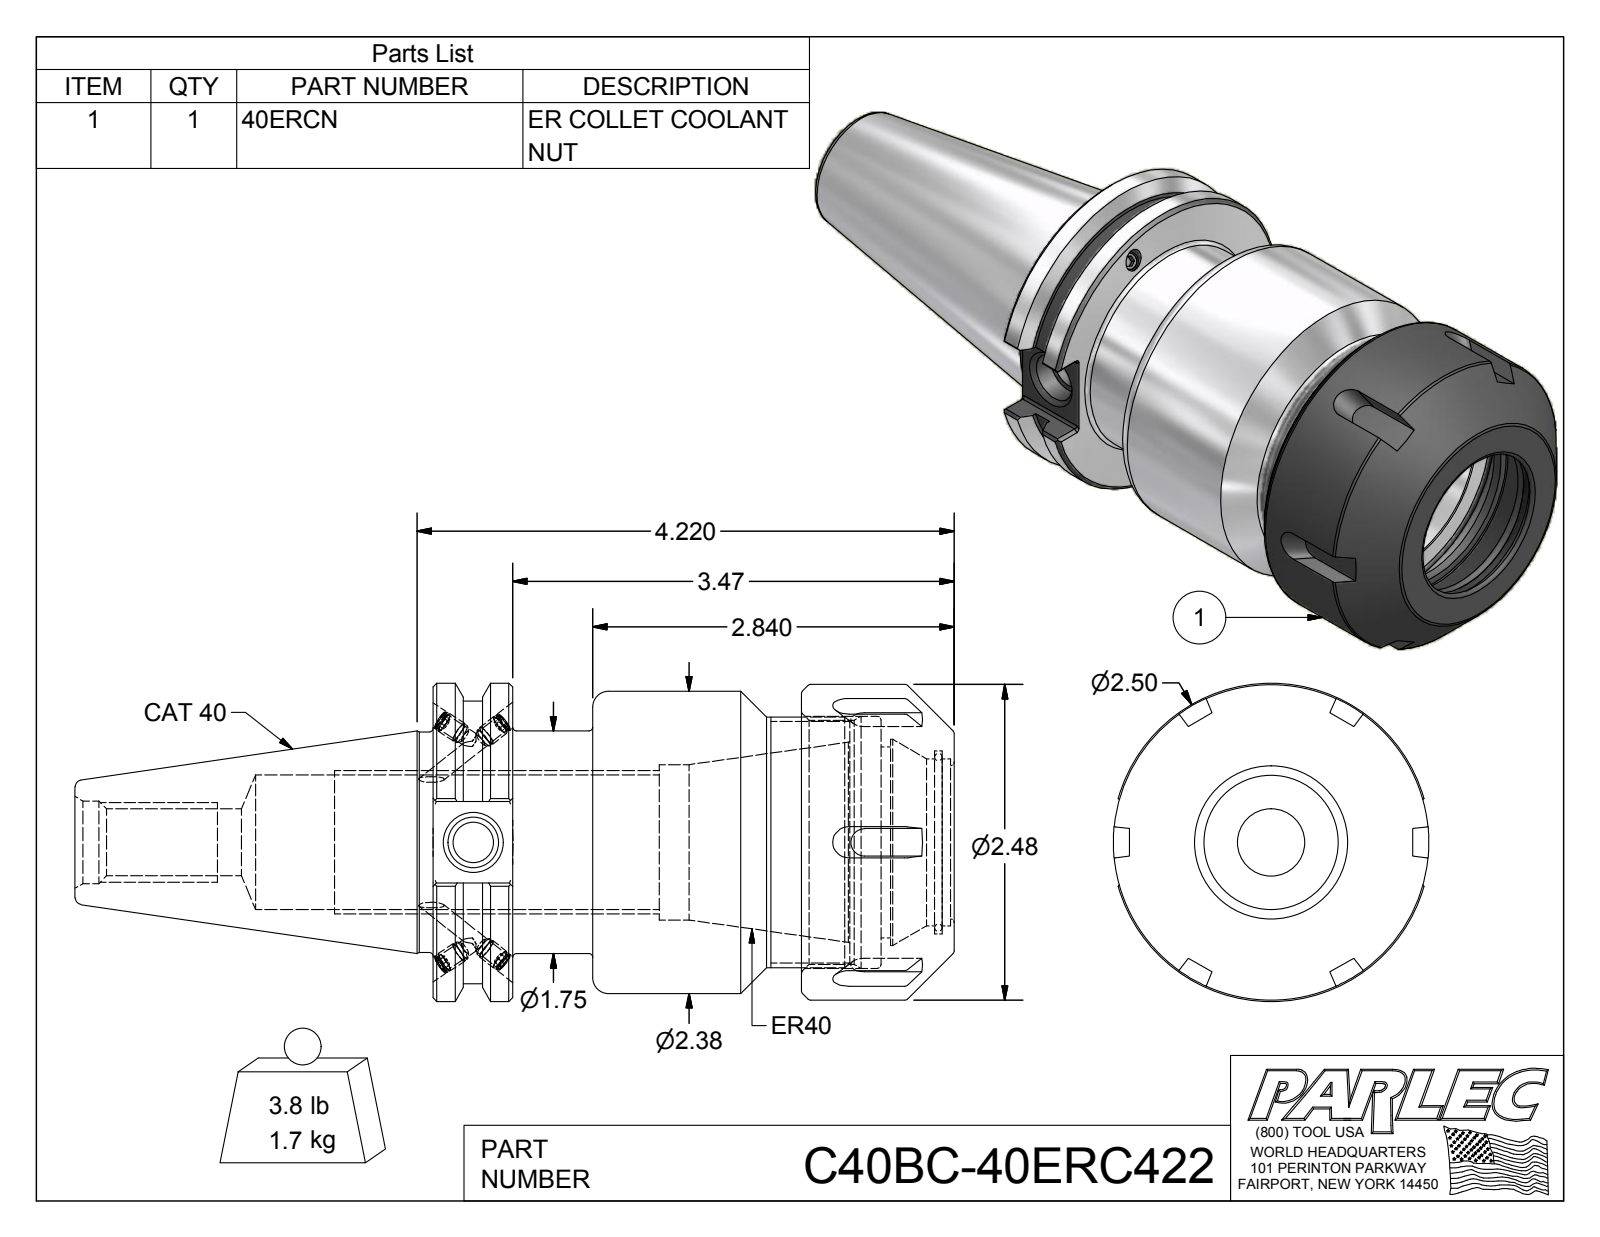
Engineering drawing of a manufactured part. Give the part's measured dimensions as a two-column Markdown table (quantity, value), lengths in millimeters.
| quantity | value |
| --- | --- |
| part name | C40BC-40ERC422; C40BCB-40ER4-1; 029-965; 40ERCN |
| STEP written by | Autodesk Inventor 2012 (AUTOMOTIVE_DESIGN) |
| units | millimeters |
| bodies | 6 solids, 223 faces (103 planar, 56 cylindrical, 64 other) |
| overall size | 175.5 × 63.5 × 63 |
| volume | 218 400 mm³ |
| surface area | 57 100 mm² |
| round holes (diameter × count) | 3.3 × 4, 4.1 × 4, 8 × 1, 10.1 × 1, 13.4 × 1, 16.5 × 1, 26.8 × 1, 31 × 1, 33.4 × 1, 36.5 × 1, 38.1 × 1, 41.1 × 1 |
| round bosses / shafts (diameter × count) | 4.2 × 4, 4 × 4, 63.5 × 1, 63 × 1, 60.3 × 1, 56.4 × 1, 50 × 1, 44.5 × 1 |
| partial cylindrical surfaces (radius × count) | 0.5 × 12 |
| main face-to-face distances | 15.9, 73.5, 89.4, 104, 88.1, 14.6, 31.9, 16, 57.5, 72.1 |
